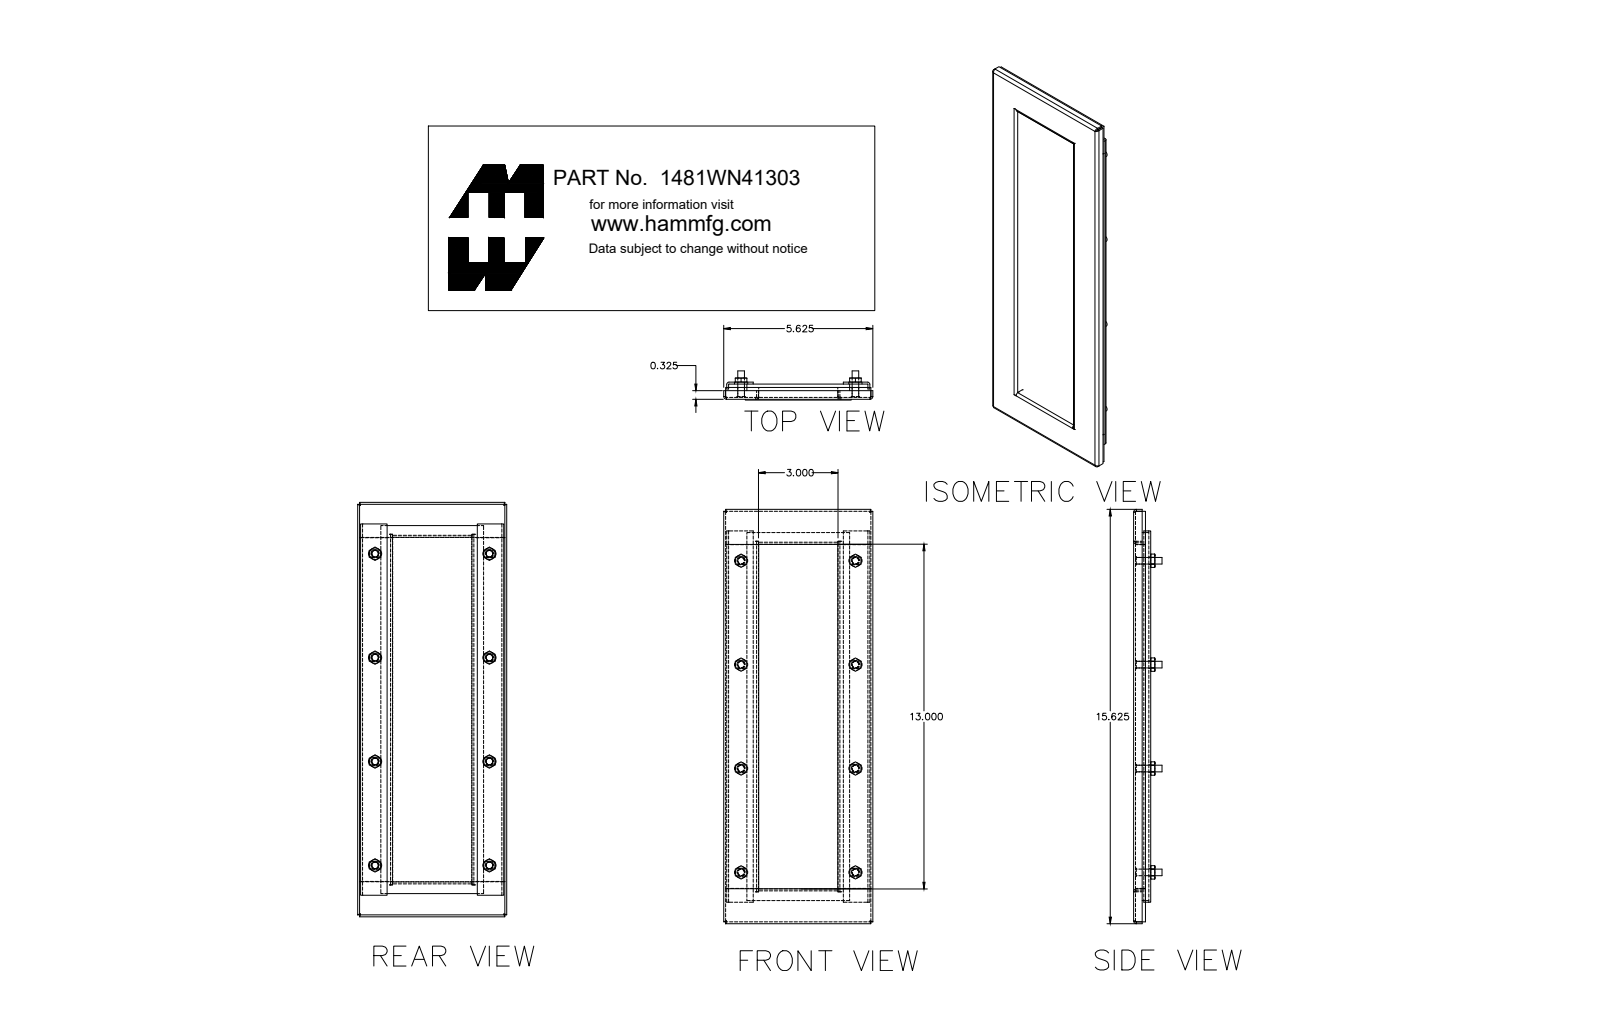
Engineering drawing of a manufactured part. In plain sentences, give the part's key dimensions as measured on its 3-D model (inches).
The part is named "1481WN41303_Default". Its 3-D file was written by "SolidWorks 2019 (CONFIG_CONTROL_DESIGN)". It is 21 solids with 382 faces: 186 planar, 84 cylindrical and 112 other. Overall it measures 16.025 by 6.025 by 1.072 inches. Its volume is 25.56 cubic inches and its surface area 466.4 square inches. Round holes: 8 of diameter 0.25, 8 of diameter 0.328. Round bosses or shafts: 8 of diameter 0.313, 8 of diameter 0.25. Partial cylindrical surfaces (rounded edges, fillets, slot ends): 8 of radius 0.036, 8 of radius 0.108, 2 of radius 0.016, 2 of radius 0.088. The main face-to-face distances are 0.072, 0.575, 0.503, 0.25, 0.325, 0.253, 0.575, 0.647, 0.322, 0.072. The hole center spacings are 4.313, 3.917, 5.826, 5.826, 5.825, 3.916, 7.833, 8.942.
